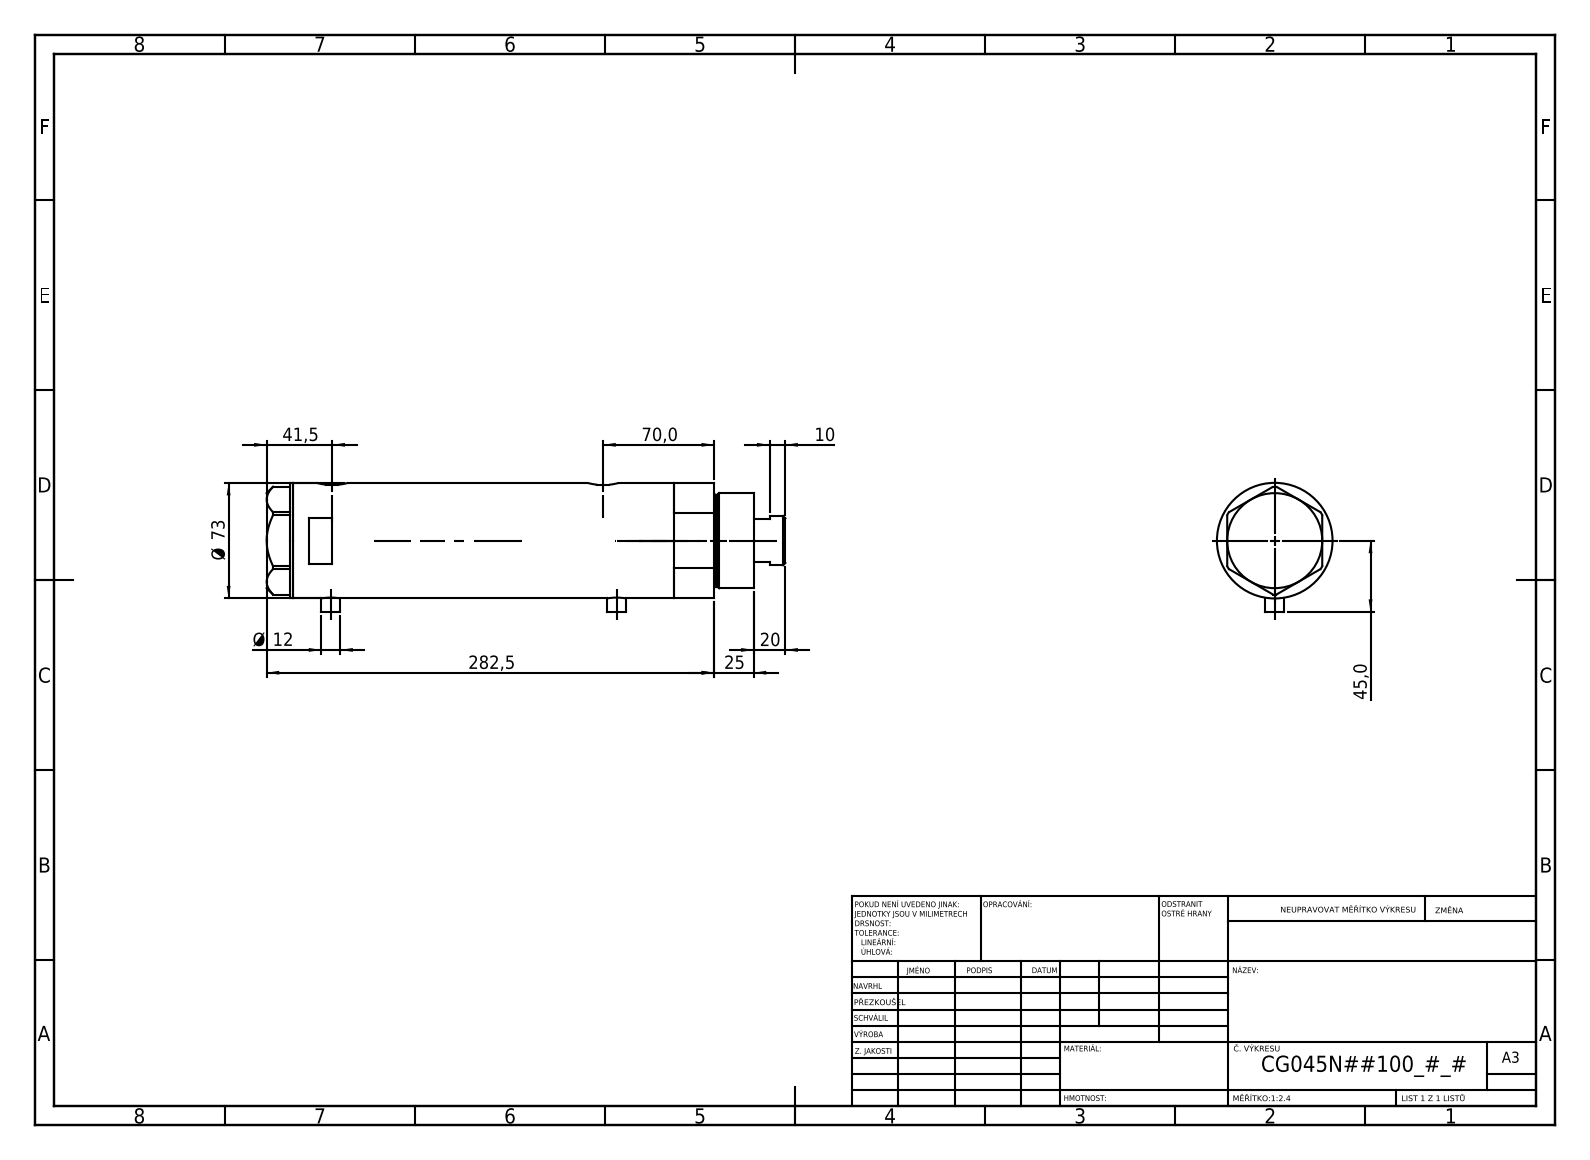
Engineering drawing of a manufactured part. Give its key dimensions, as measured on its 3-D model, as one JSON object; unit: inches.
{"part_name": "V270CG_VC; V270CG_FRONT; V270CG_MIDDLE; V270CG_BACK", "step_written_by": "SolidWorks 2019 (CONFIG_CONTROL_DESIGN)", "units": "inches", "bodies": {"solids": 4, "faces": 120, "planar": 49, "cylindrical": 51, "other": 20}, "overall_size": [12.894, 3.209, 2.874], "volume_in3": 70.85, "surface_area_in2": 287.2, "round_holes": [[0.492, 2], [0.518, 2], [0.413, 1], [1.26, 1], [1.319, 1], [1.772, 1], [1.89, 1], [2.52, 1]], "round_bosses_or_shafts": [[0.472, 2], [2.874, 1], [2.362, 1], [2.283, 1], [1.22, 1]], "partial_cylinders_radius": [[0.394, 2]], "face_to_face_distances": [6.693, 7.717, 1.024, 0.65, 1.673, 8.366, 0.079, 11.457, 2.756, 12.106], "hole_center_spacings": [0.039, 0.335, 6.732, 6.772, 7.067, 7.106]}
